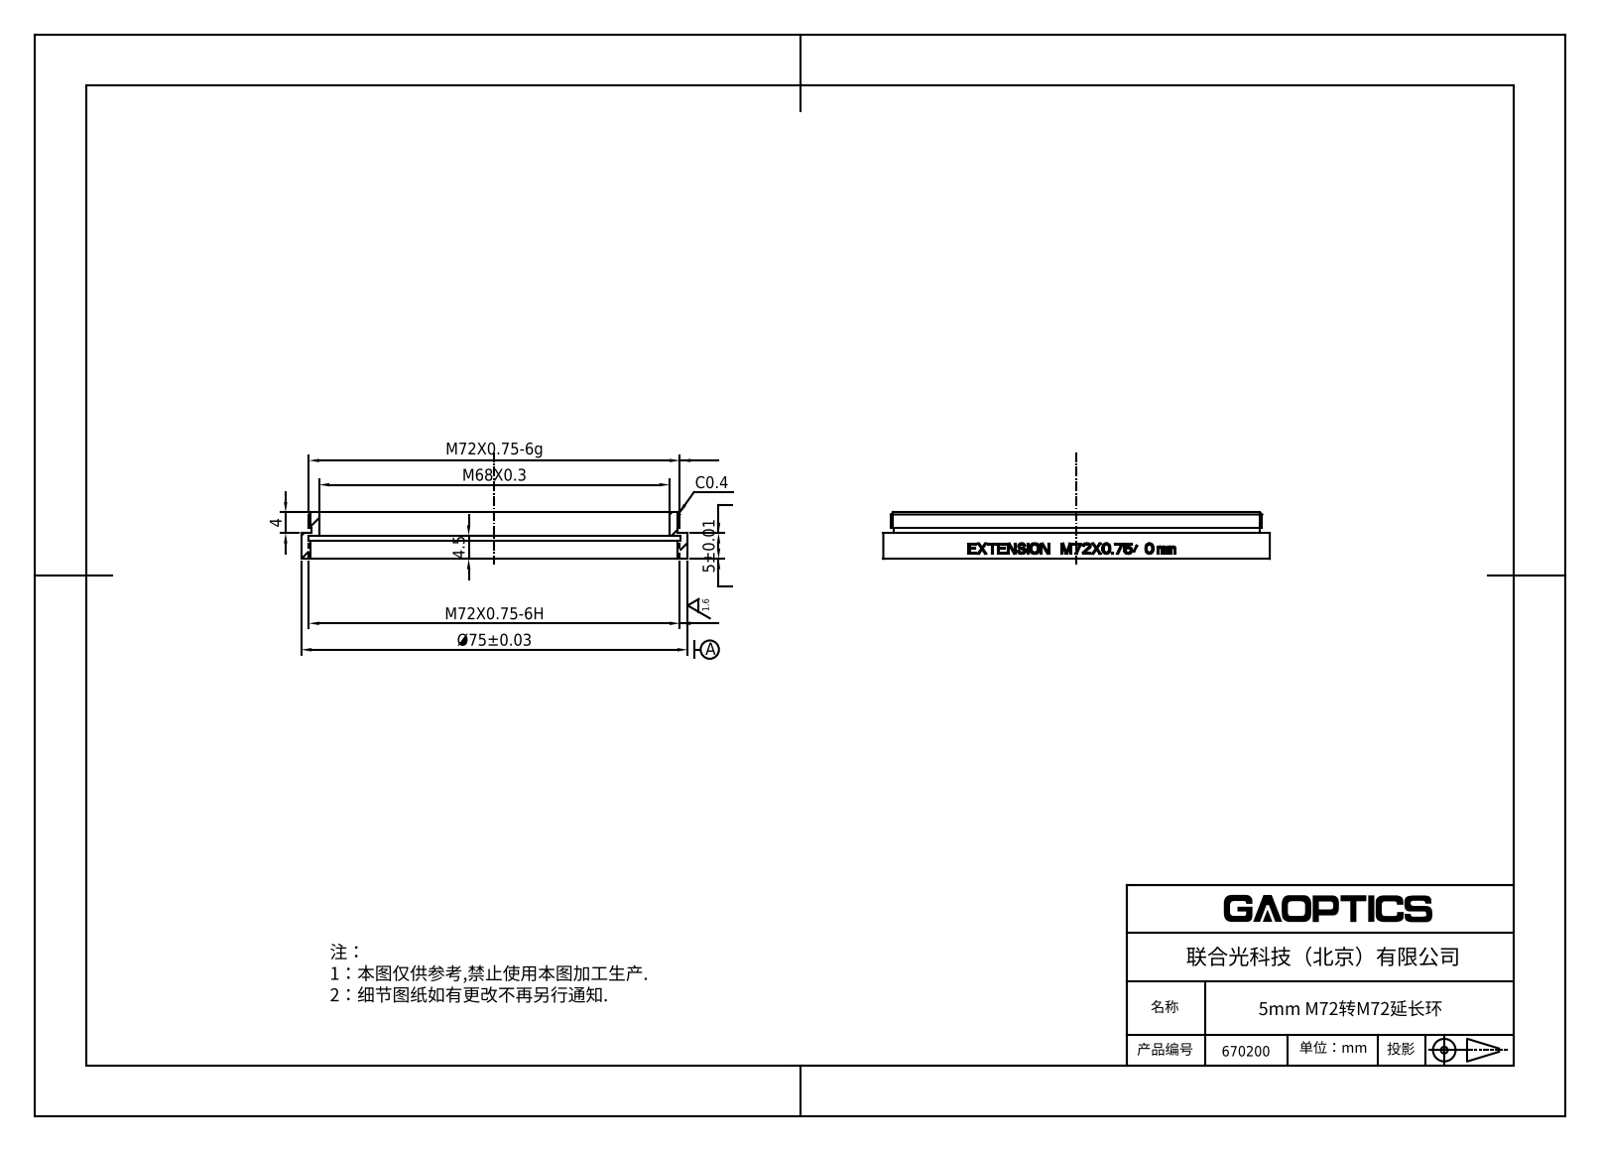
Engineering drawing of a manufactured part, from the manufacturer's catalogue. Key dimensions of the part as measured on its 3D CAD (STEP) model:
Part name (STEP PRODUCT): 5mm
STEP written by: SolidWorks 2019 (CONFIG_CONTROL_DESIGN)
Units: millimetres
Bodies: 1 solid, 55 faces (6 planar, 43 cylindrical, 6 other)
Overall size (bounding box): 75 × 75 × 9
Volume: 3 706 mm³ · Surface area: 6 338 mm²
Round holes (diameter × count): ⌀68 ×1, ⌀71.2 ×1, ⌀72.2 ×1
Round bosses / shafts (diameter × count): ⌀75 ×1, ⌀72 ×1, ⌀71 ×1
Main face-to-face distances: 4.5, 0.5, 5, 9, 4, 1, 1.5, 3.5, 5.5, 6
